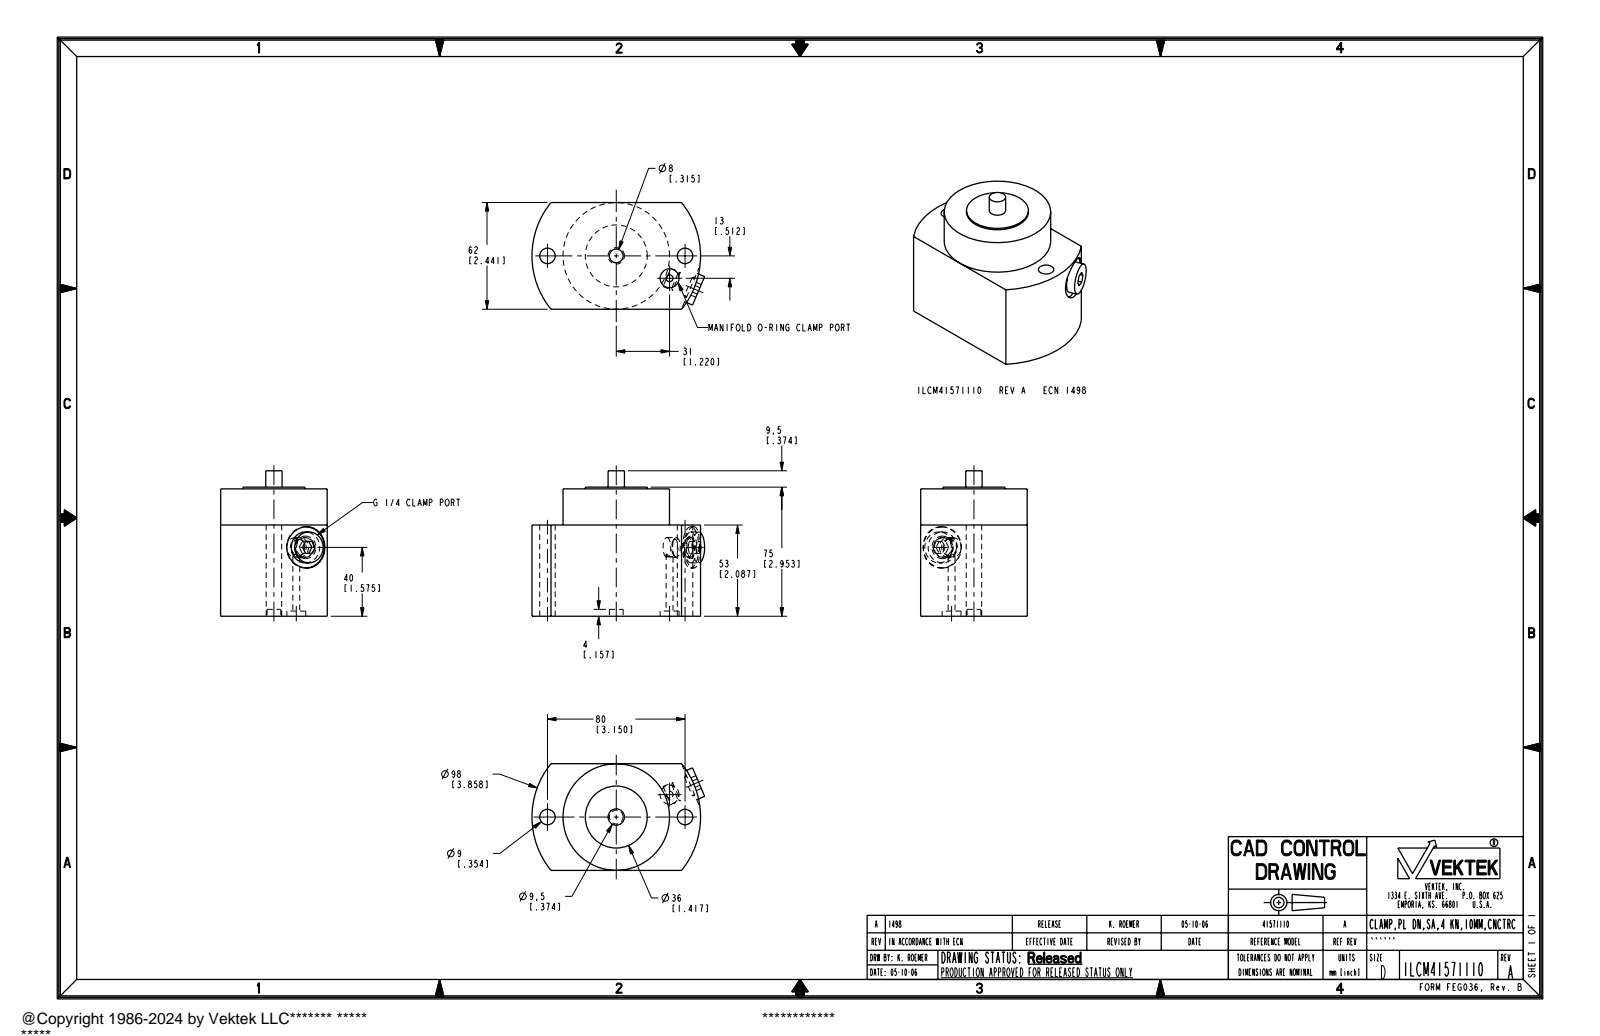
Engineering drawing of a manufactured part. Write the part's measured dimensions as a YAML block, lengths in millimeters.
part_name: "ILCM41571110"
step_written_by: "PRO/ENGINEER BY PARAMETRIC TECHNOLOGY CORPORATION, 2004290 (AUTOMOTIVE_DESIGN_CC2)"
units: millimeters
bodies: {solids: 1, faces: 52, planar: 22, cylindrical: 26, other: 4}
overall_size: [100.38, 84.5, 62]
volume: 356055
surface_area: 35326
round_holes:
  - {diameter: 9, count: 2}
  - {diameter: 4, count: 1}
  - {diameter: 8, count: 1}
  - {diameter: 11, count: 1}
  - {diameter: 11.45, count: 1}
  - {diameter: 24, count: 1}
round_bosses_or_shafts:
  - {diameter: 61.9, count: 1}
  - {diameter: 36, count: 1}
  - {diameter: 18, count: 1}
  - {diameter: 9.5, count: 1}
partial_cylinders:
  - {radius: 49, count: 1}
face_to_face_distances: [62, 53, 74, 21, 1, 75, 22, 5, 15.01, 71]
hole_center_spacings: [40, 15.81, 33.62, 72.18, 80]
